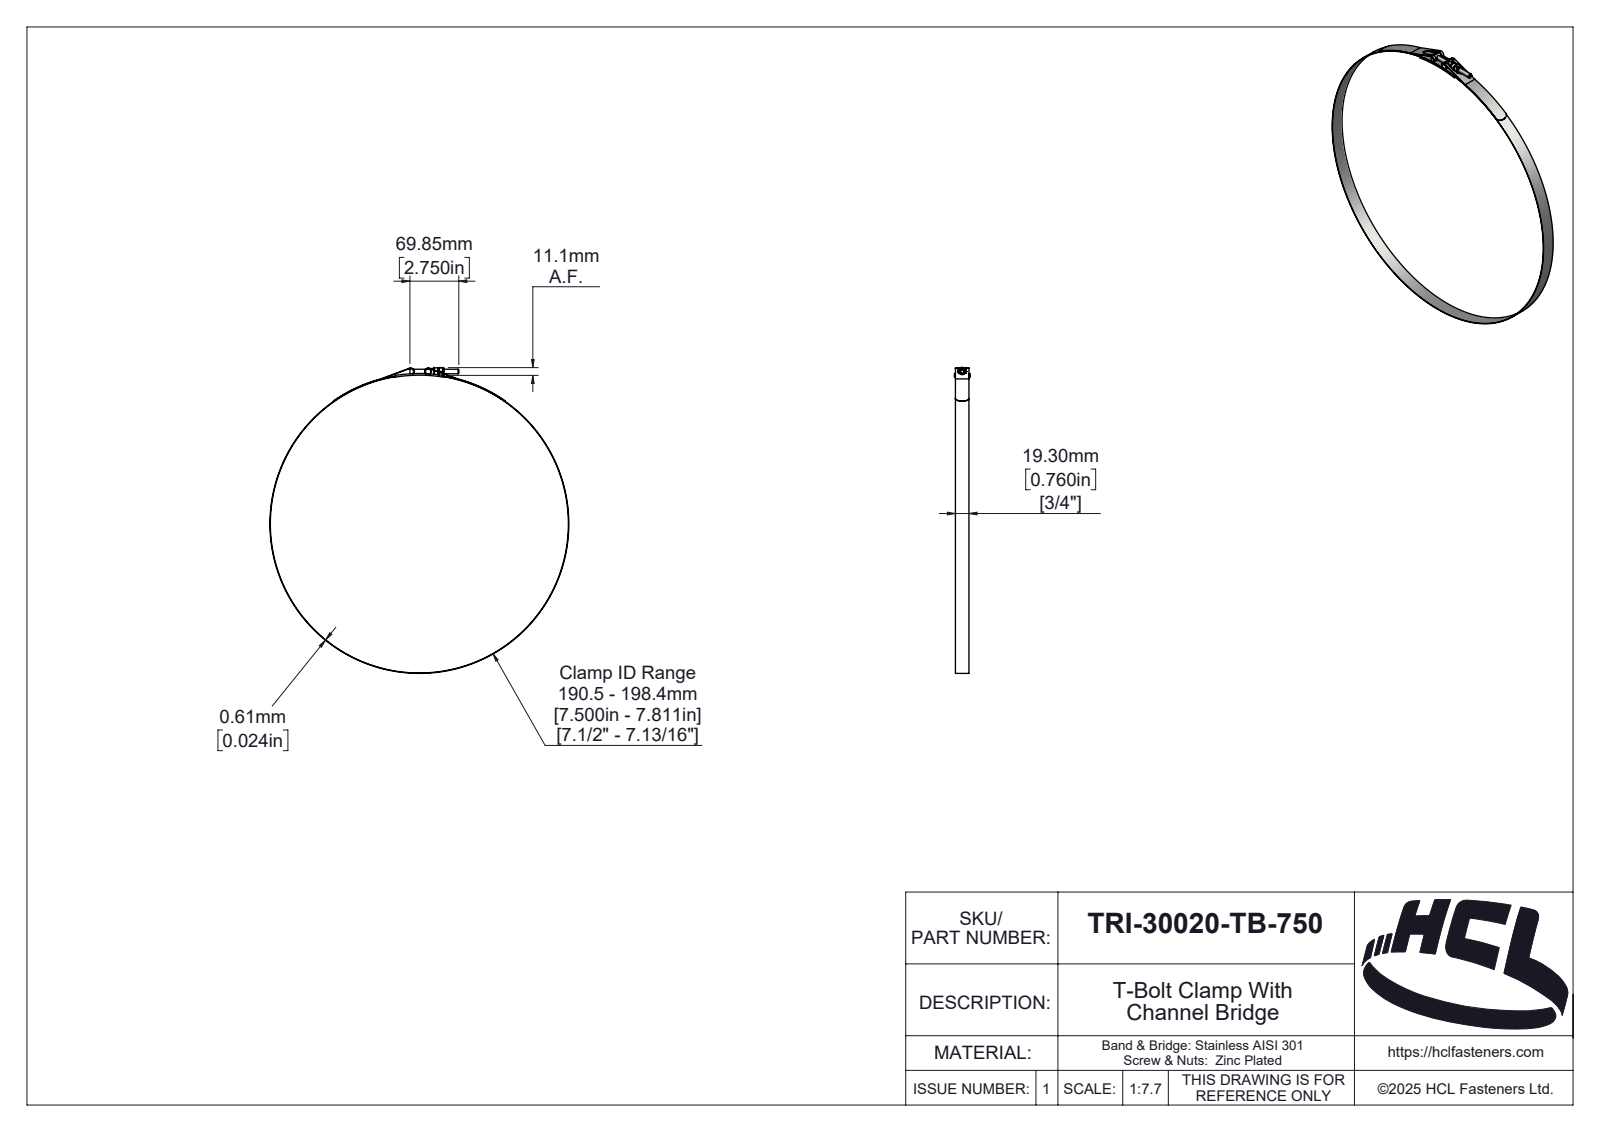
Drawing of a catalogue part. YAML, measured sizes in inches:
part_name: "TRI-30020-TB-750"
step_written_by: "SolidWorks 2025 (AUTOMOTIVE_DESIGN)"
units: inches
bodies: {solids: 6, faces: 330, planar: 44, cylindrical: 122, other: 164}
overall_size: [17.204, 16.82, 0.866]
volume: 1.429
surface_area: 107.8
round_holes:
  - {diameter: 0.213, count: 1}
  - {diameter: 0.25, count: 1}
  - {diameter: 0.256, count: 1}
  - {diameter: 0.298, count: 1}
  - {diameter: 16.772, count: 1}
round_bosses_or_shafts:
  - {diameter: 0.338, count: 2}
  - {diameter: 16.82, count: 1}
  - {diameter: 0.417, count: 1}
partial_cylinders:
  - {radius: 0.015, count: 6}
  - {radius: 0.02, count: 2}
  - {radius: 0.173, count: 2}
  - {radius: 0.197, count: 2}
  - {radius: 0.023, count: 1}
  - {radius: 0.095, count: 1}
  - {radius: 0.119, count: 1}
  - {radius: 0.126, count: 1}
face_to_face_distances: [0.024, 0.76, 0.053, 0.813, 0.029, 0.842, 0.789, 0.866, 0.818, 1.614]
hole_center_spacings: [8.583]
